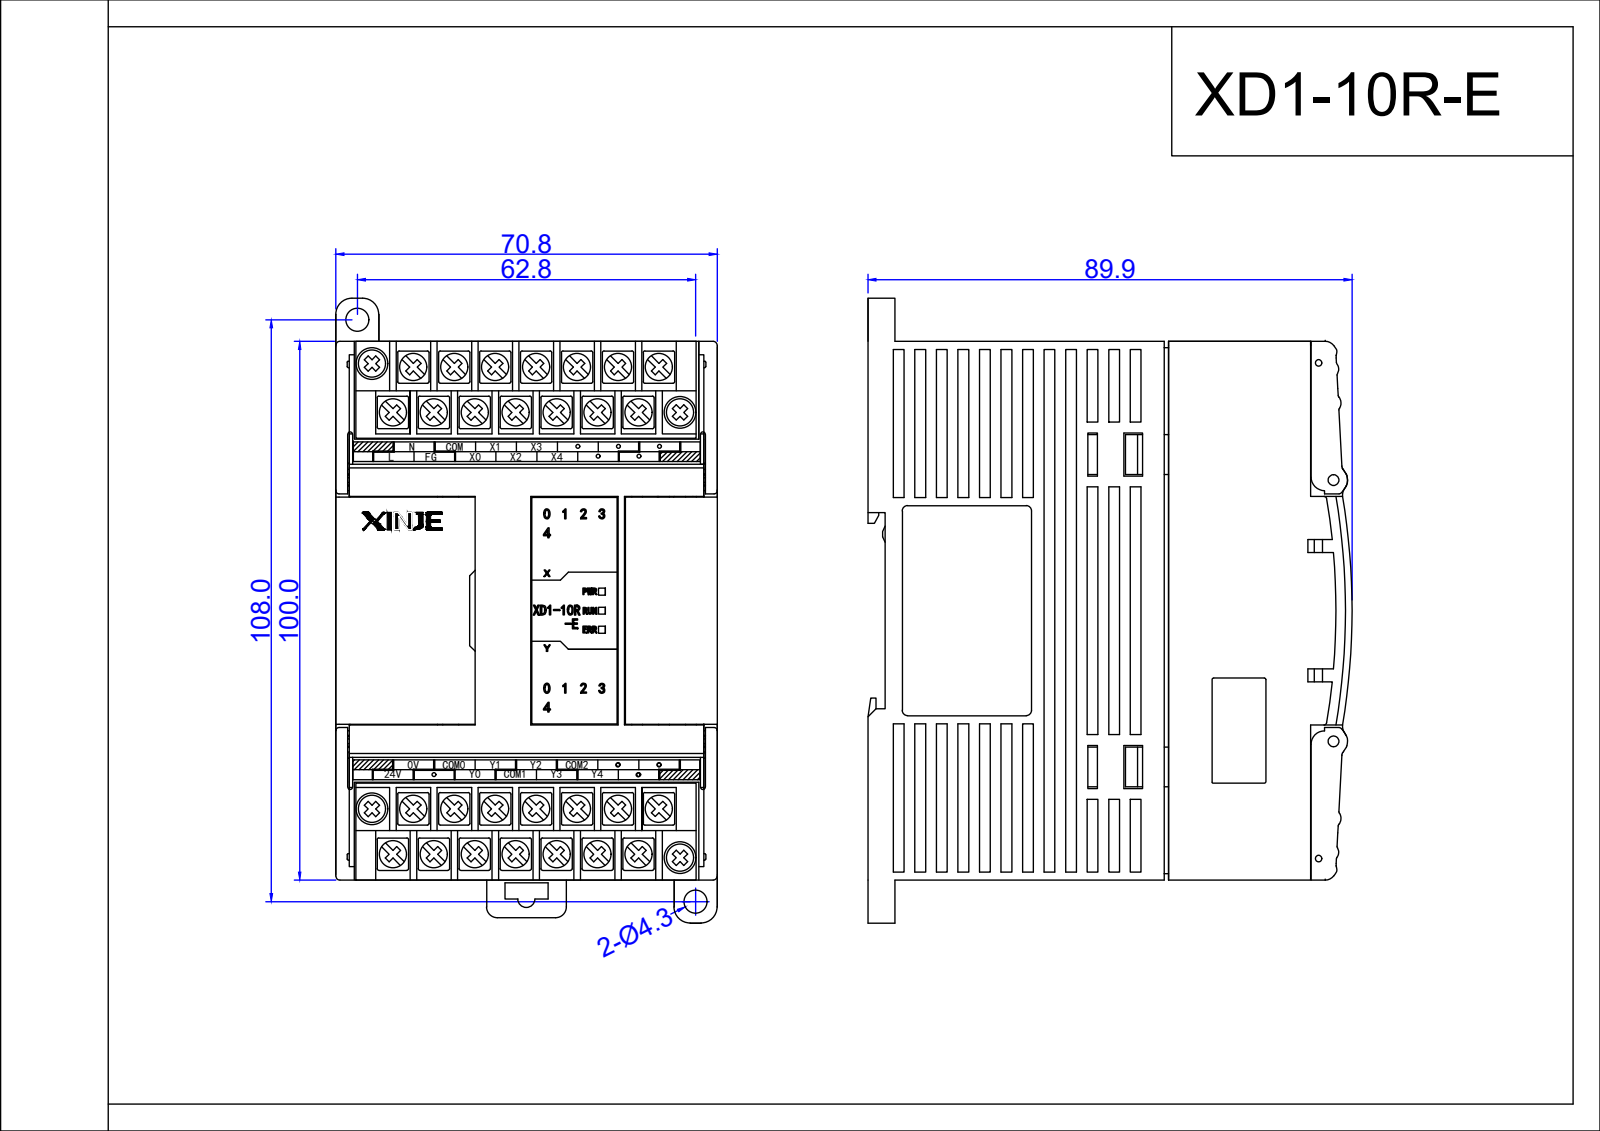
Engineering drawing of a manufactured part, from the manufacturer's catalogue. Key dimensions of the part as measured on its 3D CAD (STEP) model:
STEP written by: ST-DEVELOPER v16.5 (CONFIG_CONTROL_DESIGN)
Units: millimetres
Bodies: 2 solids, 3089 faces (2085 planar, 689 cylindrical, 315 other)
Overall size (bounding box): 116 × 89.69 × 70.6
Volume: 576 100 mm³ · Surface area: 70 256 mm²
Round holes (diameter × count): ⌀3.45 ×28, ⌀4.3 ×2
Round bosses / shafts (diameter × count): ⌀5.4 ×32, ⌀3 ×28, ⌀2.5 ×28
Partial cylindrical surfaces — rounded edges, fillets, slot ends (radius × count): R0.25 ×112, R0.2 ×60, R0.5 ×16, R0.75 ×8, R1 ×8, R0.1 ×4, R0.3 ×4, R0.45 ×4
Main face-to-face distances: 70.6, 70.3, 3.2, 100, 18.1, 81.9, 2.2, 68.1, 62.71, 0.75
Hole centre spacings: 9.22, 7.6, 82.35, 15.2, 83.4, 22.8, 85.11, 82
